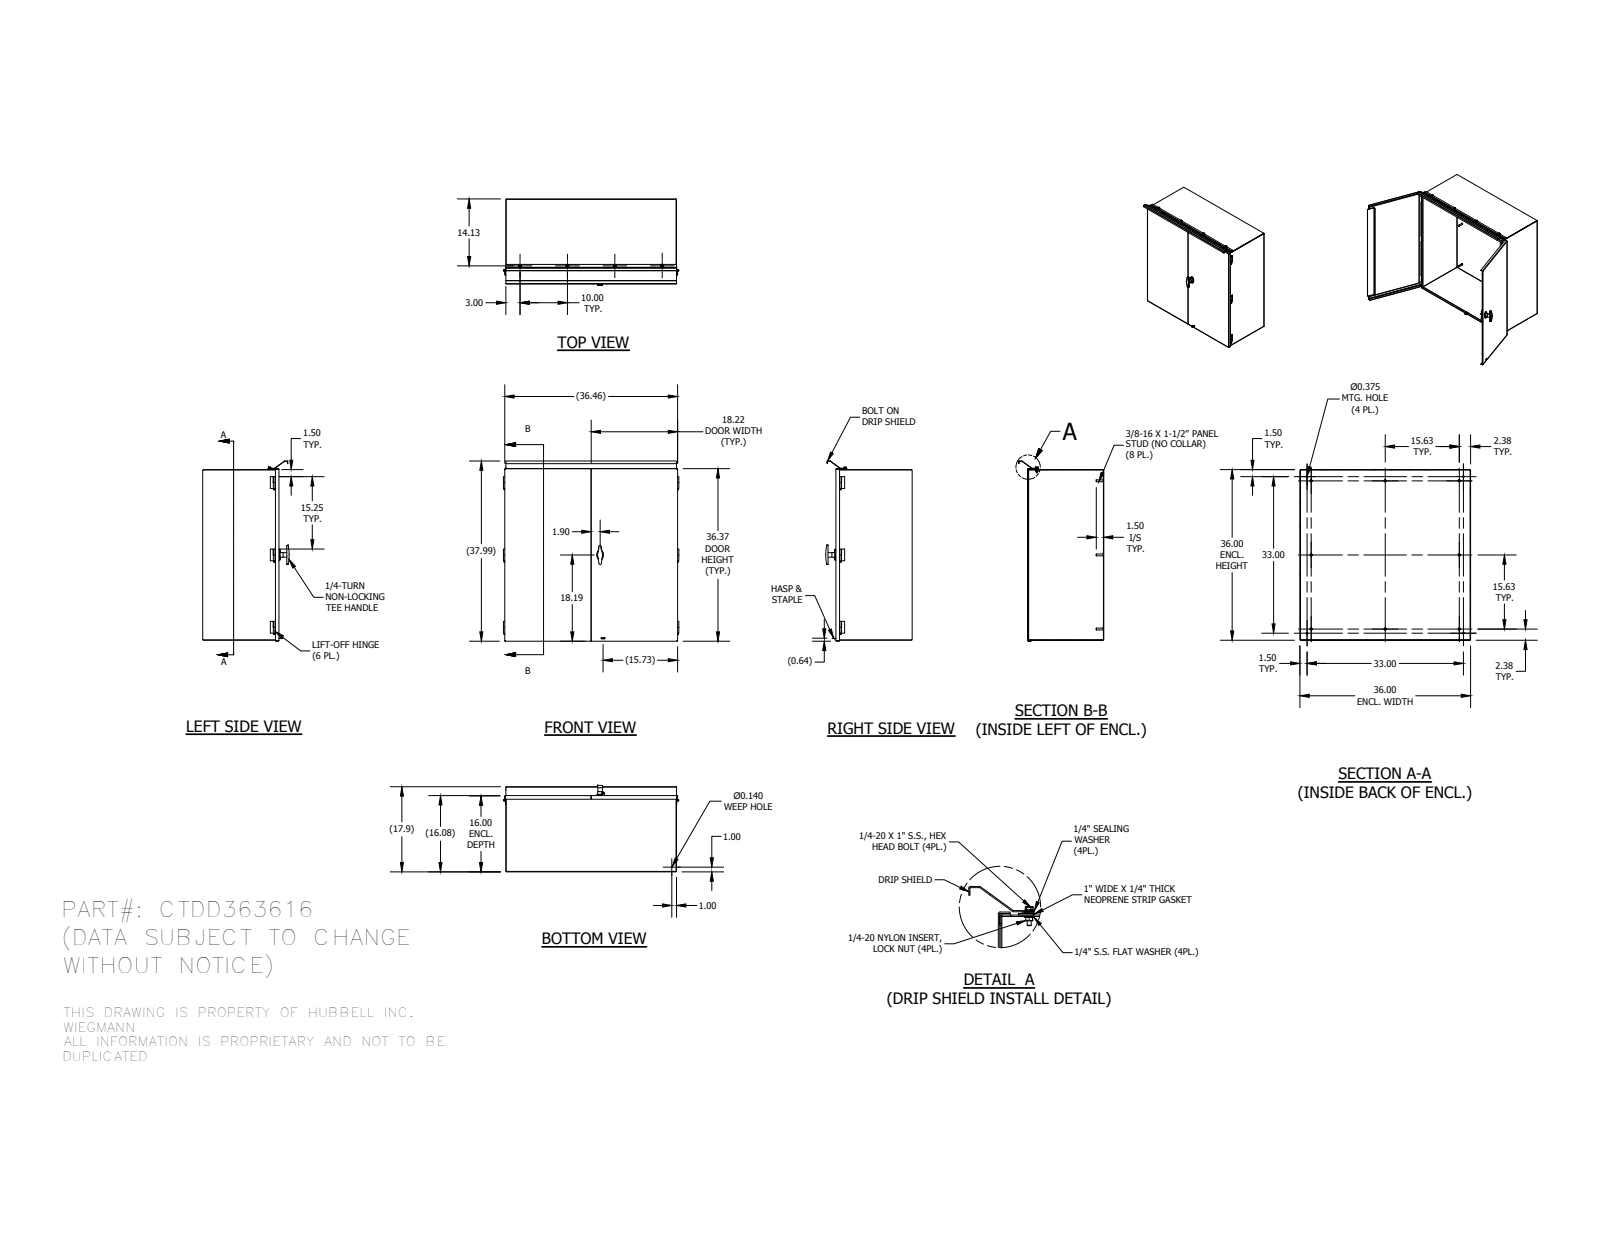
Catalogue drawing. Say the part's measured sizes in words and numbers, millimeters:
The part is named "CTDD363616BLR; CTDD3616TOP; CTDD3616BTM; 38822 (+8 more)". Its 3-D file was written by "Autodesk Inventor 2014 (AUTOMOTIVE_DESIGN)". It is 67 solids with 1098 faces: 642 planar, 230 cylindrical and 226 other. Overall it measures 965.07 by 939.8 by 463.15 millimeters. Its volume is 8 619 000 cubic millimeters and its surface area 7 296 000 square millimeters. Round holes: 6 of diameter 4.98, 6 of diameter 7.14, 5 of diameter 9.52, 4 of diameter 5.97, 4 of diameter 6.99, 4 of diameter 7.37, 2 of diameter 4.06, 2 of diameter 5.36, 2 of diameter 5.56, 2 of diameter 6.35, 2 of diameter 7.14, 1 of diameter 2.38. Round bosses or shafts: 8 of diameter 11.73, 8 of diameter 9.52, 6 of diameter 11.13, 6 of diameter 6.35, 4 of diameter 16.51, 4 of diameter 15.88, 4 of diameter 15.24, 4 of diameter 6.6. Partial cylindrical surfaces (rounded edges, fillets, slot ends): 23 of radius 0.79, 13 of radius 3.17, 6 of radius 2.67, 6 of radius 3.17, 3 of radius 1.59, 3 of radius 1.59, 2 of radius 0.2, 2 of radius 3.97. The main face-to-face distances are 2.38, 406, 912.02, 403.62, 408.38, 2.37, 914.4, 909.64, 914.39, 909.65. The hole center spacings are 838.2, 254, 19.05, 508, 545.73, 559.85, 574.25, 614.93.
